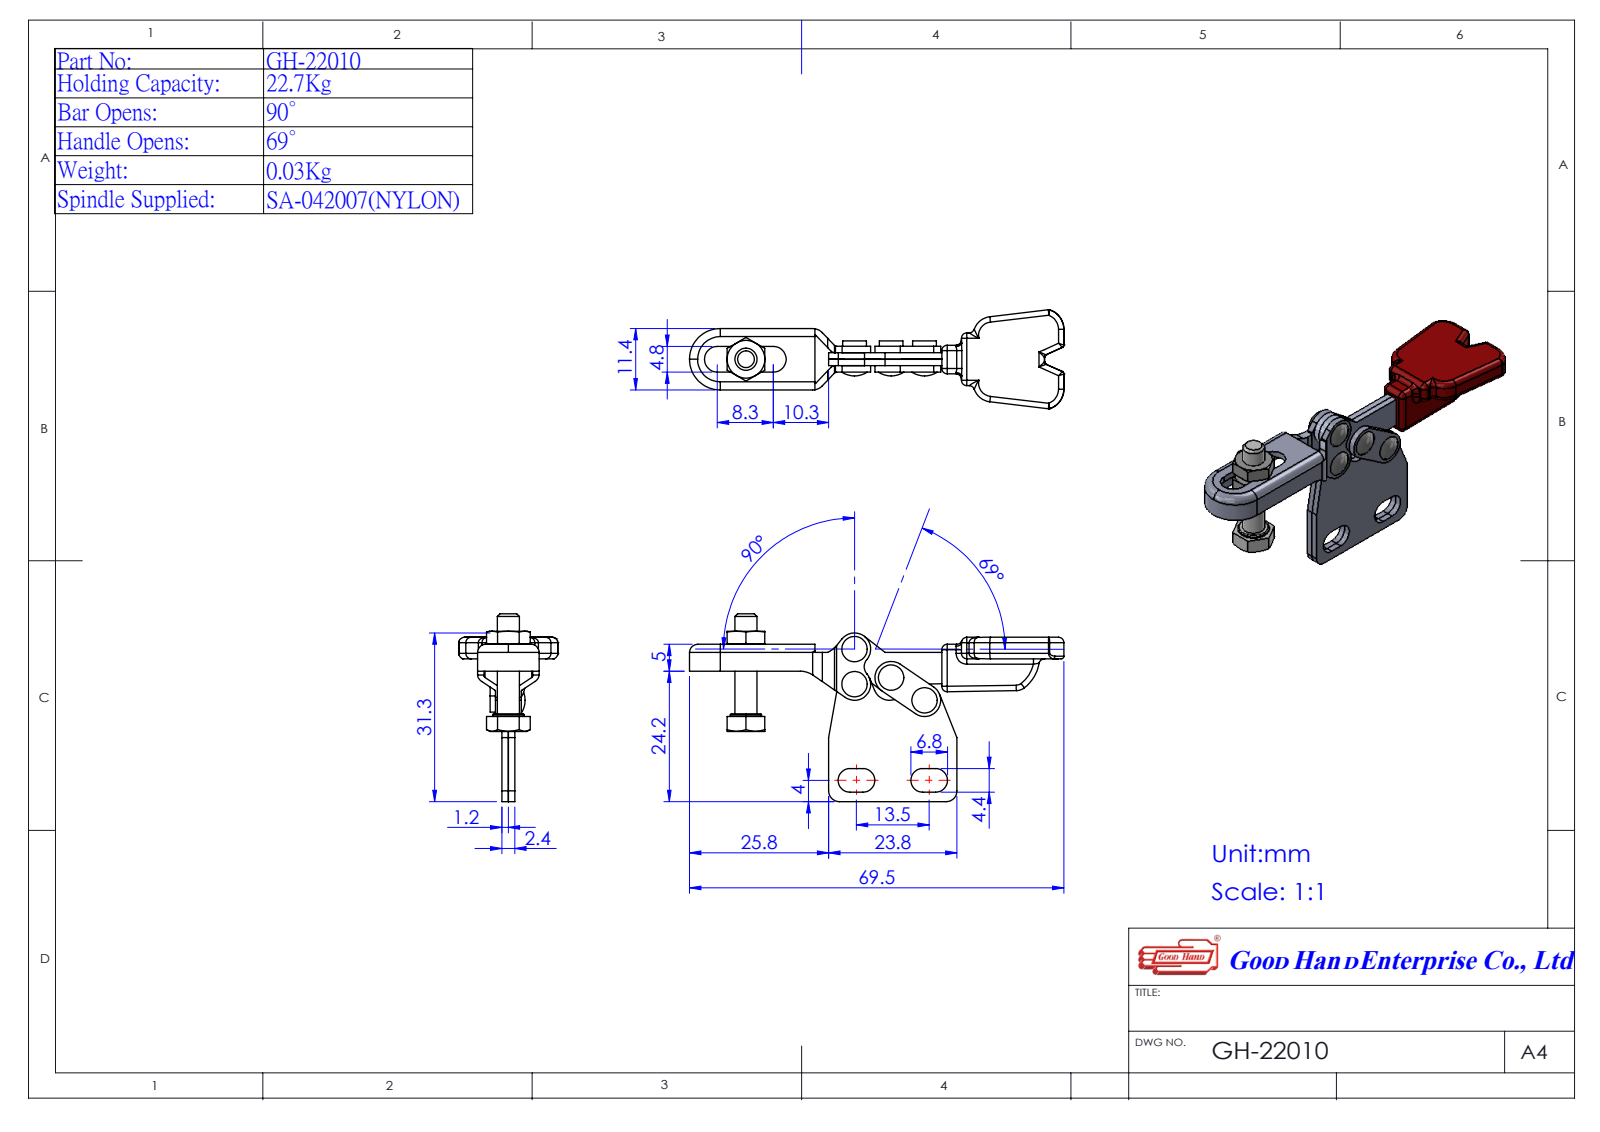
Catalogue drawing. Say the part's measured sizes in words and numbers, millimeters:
The part is named "12201014(簡化); GH-22010(簡化); Group2^GH-22010(簡化); Group3^GH-22010(簡化) (+2 more)". Its 3-D file was written by "SolidWorks 2016 (AUTOMOTIVE_DESIGN)". It is 6 solids with 306 faces: 128 planar, 130 cylindrical and 48 other. Overall it measures 69.5 by 36.3 by 18.39 millimeters. Its volume is 4 547 cubic millimeters and its surface area 6 189 square millimeters. Round holes: 4 of diameter 2. Round bosses or shafts: 4 of diameter 3.5, 1 of diameter 6, 1 of diameter 5.8, 1 of diameter 4.1. Partial cylindrical surfaces (rounded edges, fillets, slot ends): 20 of radius 1, 5 of radius 0.5, 5 of radius 3, 4 of radius 2, 4 of radius 2.2, 3 of radius 2.5, 2 of radius 2.38, 2 of radius 3.5. The main face-to-face distances are 1.2, 2.4, 4.5, 5.7, 6.9, 3.3, 1.5, 2.7, 1.3, 3.6. The hole center spacings are 6.5, 6.91, 7.49, 8.62, 13.34, 16.1.
